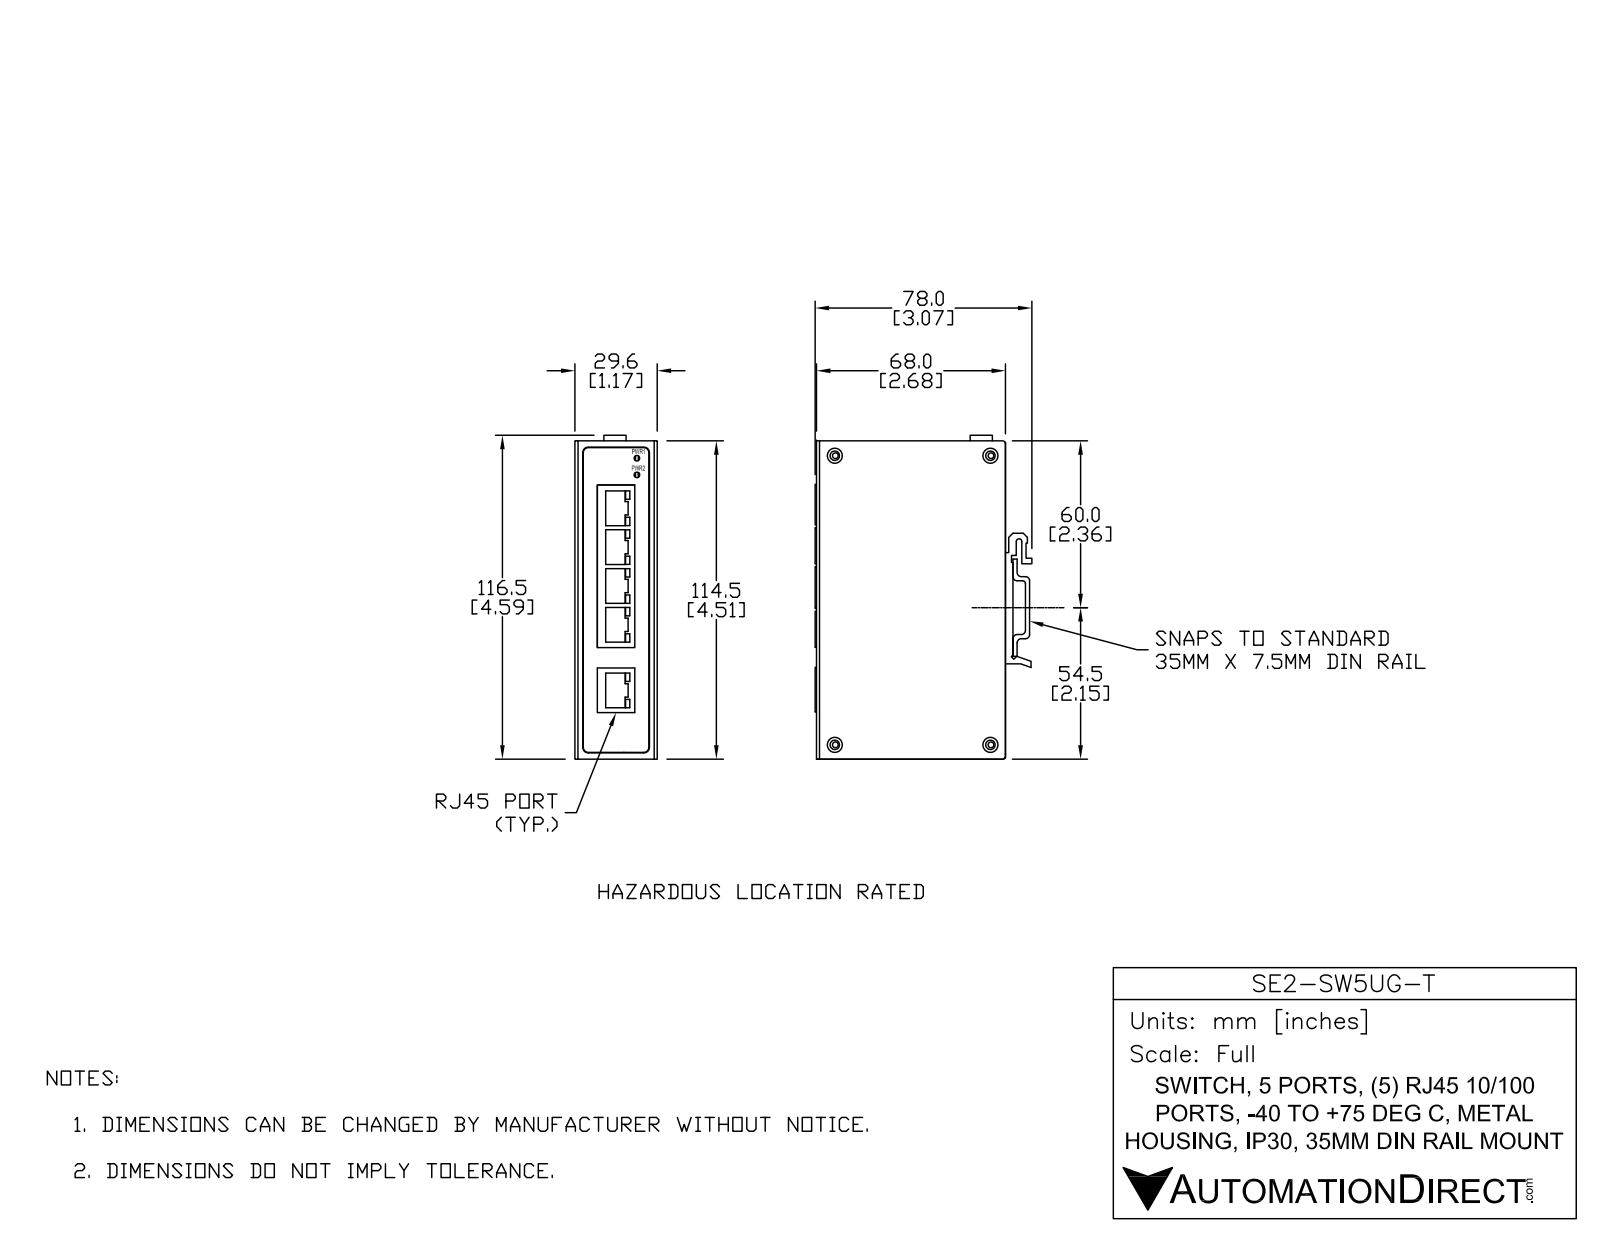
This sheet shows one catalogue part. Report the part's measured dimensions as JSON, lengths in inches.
{"part_name": "SE2-SW5UG-T", "step_written_by": "SolidWorks 2017 (AUTOMOTIVE_DESIGN)", "units": "inches", "bodies": {"solids": 10, "faces": 938, "planar": 648, "cylindrical": 245, "other": 45}, "overall_size": [4.951, 3.047, 1.165], "volume_in3": 3.531, "surface_area_in2": 134.7, "round_holes": [[0.051, 4], [0.11, 4], [0.15, 4], [0.122, 3], [0.118, 2], [0.138, 2], [0.155, 1]], "round_bosses_or_shafts": [[0.142, 4], [0.118, 4], [0.051, 4], [0.024, 4], [0.197, 2], [0.315, 1], [0.157, 1]], "partial_cylinders_radius": [[0.024, 96], [0.026, 16], [0.079, 8], [0.118, 8], [0.041, 6], [0.039, 5], [0.012, 4], [0.112, 4]], "face_to_face_distances": [0.039, 0.02, 1.087, 1.126, 0.079, 1.047, 1.067, 1.106, 0.059, 1.028], "hole_center_spacings": [0.2, 2.205, 0.203, 0.4, 0.4, 0.543, 0.543, 0.574]}
